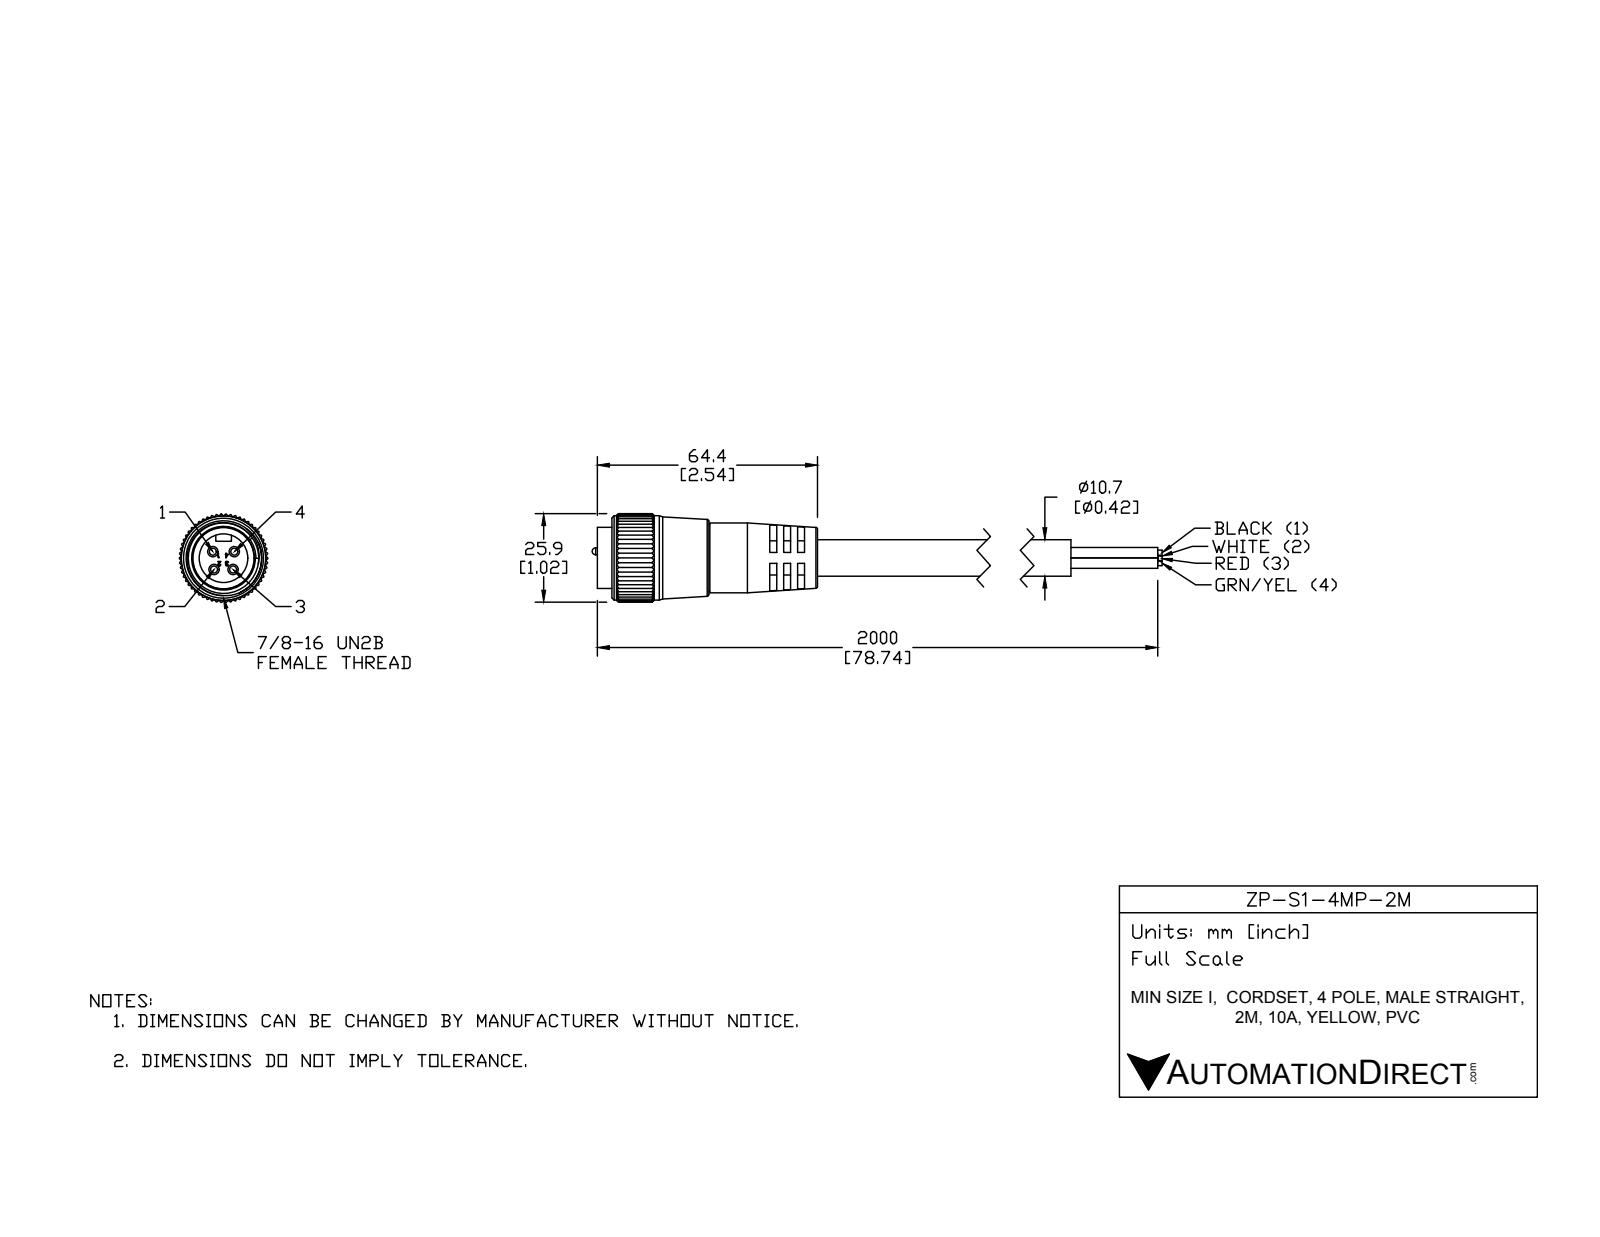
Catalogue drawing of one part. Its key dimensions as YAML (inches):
part_name: "ZP-S1-4MP-2M"
step_written_by: "SolidWorks 2015 (AUTOMOTIVE_DESIGN)"
units: inches
bodies: {solids: 6, faces: 589, planar: 213, cylindrical: 318, other: 58}
overall_size: [4.331, 2.083, 1.017]
volume: 1.704
surface_area: 19.89
round_holes:
  - {diameter: 0.56, count: 1}
  - {diameter: 0.786, count: 1}
  - {diameter: 0.805, count: 1}
  - {diameter: 0.827, count: 1}
round_bosses_or_shafts:
  - {diameter: 0.12, count: 4}
  - {diameter: 0.079, count: 4}
  - {diameter: 0.42, count: 2}
  - {diameter: 0.972, count: 1}
  - {diameter: 0.803, count: 1}
  - {diameter: 0.768, count: 1}
  - {diameter: 0.704, count: 1}
partial_cylinders:
  - {radius: 0.01, count: 165}
  - {radius: 0.09, count: 1}
  - {radius: 0.207, count: 1}
  - {radius: 0.509, count: 1}
face_to_face_distances: [0.079, 0.159, 0.08, 0.238, 0.546, 0.468, 0.387, 0.309, 0.229, 0.317]
